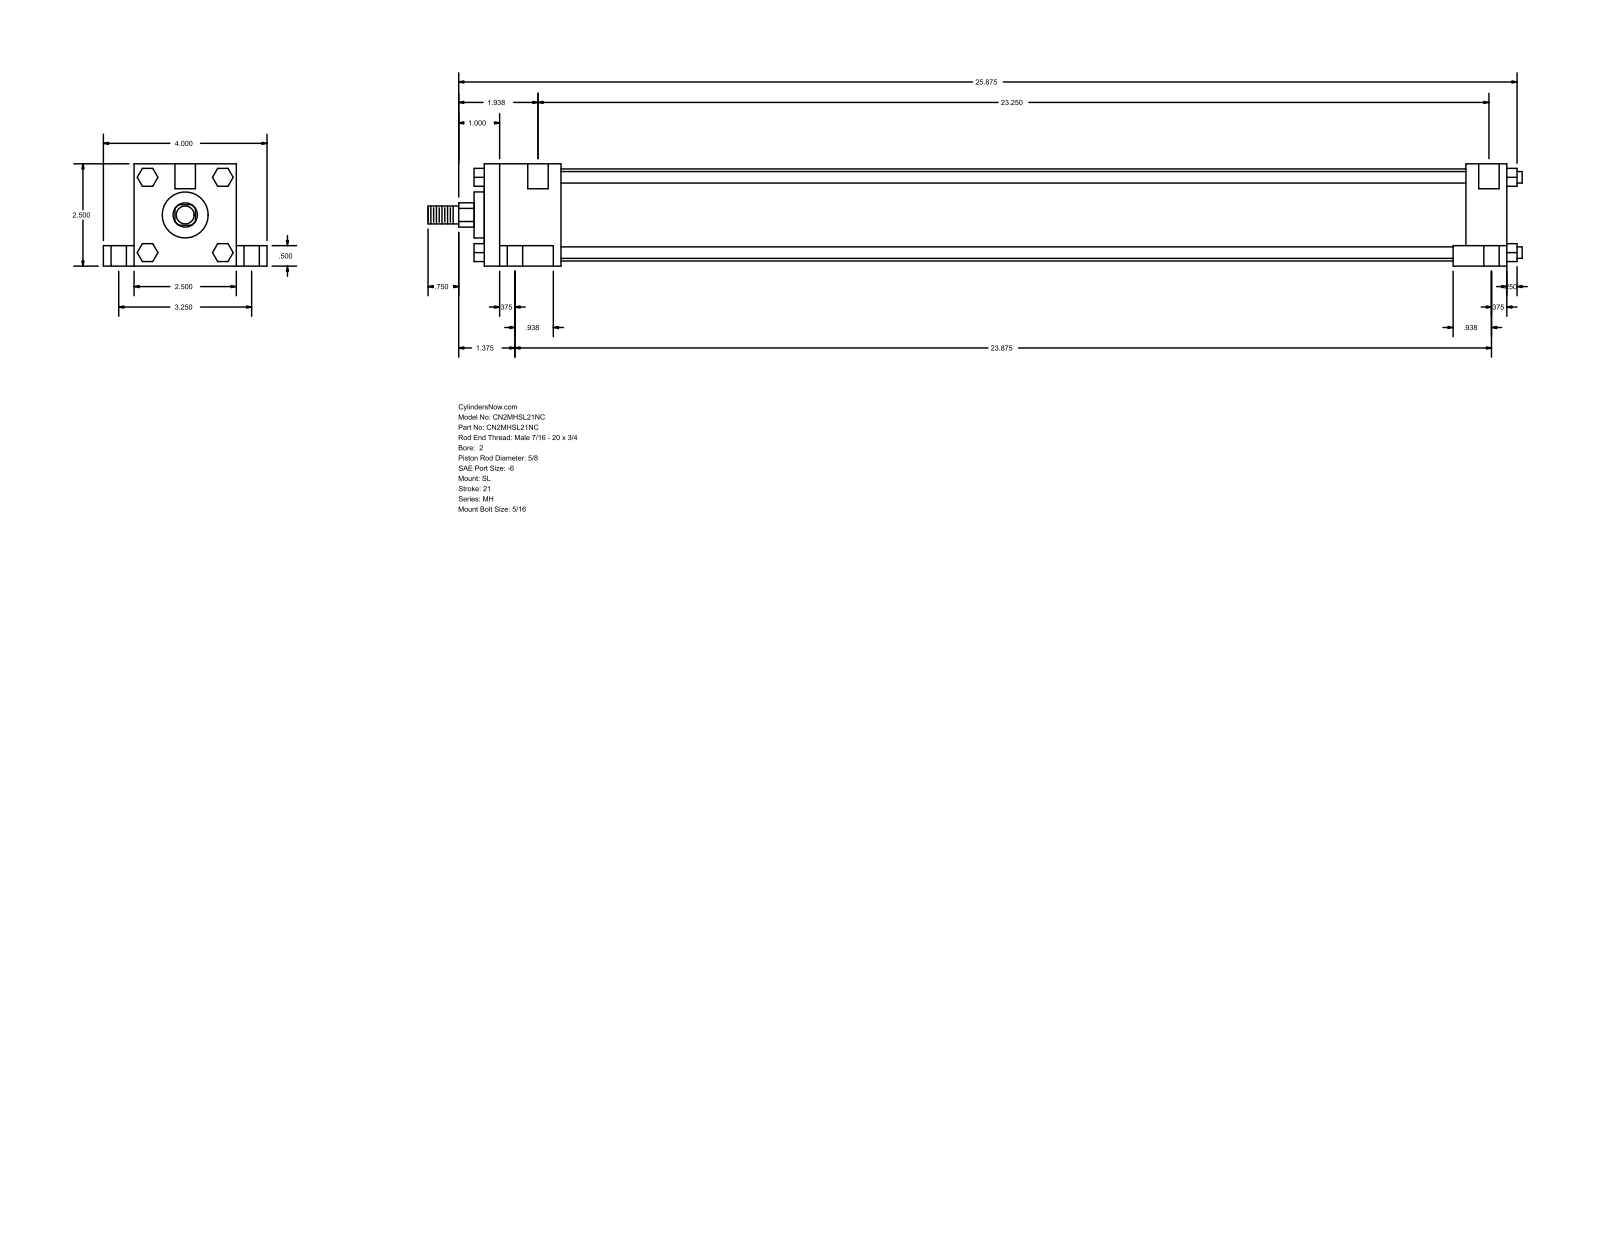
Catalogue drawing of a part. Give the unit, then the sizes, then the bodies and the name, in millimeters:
Units: millimetres
Overall size (bounding box): 679.45 × 101.6 × 63.5
Round holes (diameter × count): ⌀5.56 ×4, ⌀9.53 ×4, ⌀15.88 ×4, ⌀12.7 ×2
Round bosses / shafts (diameter × count): ⌀7.14 ×4, ⌀57.15 ×1, ⌀28.57 ×1, ⌀15.88 ×1, ⌀11.11 ×1
Partial cylindrical surfaces — rounded edges, fillets, slot ends (radius × count): R7.54 ×1
Main face-to-face distances: 63.5, 635, 12.7, 19.05, 82.55, 50.8, 25.4, 609.6, 47.62, 561.98
Hole centre spacings: 41.3, 42.36, 43.67, 82.54, 593.58, 598.33, 598.49, 606.25
Bodies: 0 solids, 148 faces (112 planar, 36 cylindrical, 0 other)
Part name (STEP PRODUCT): MH_SL__0200_0.625
STEP written by: GSSL Pune (CONFIG_CONTROL_DESIGN)
